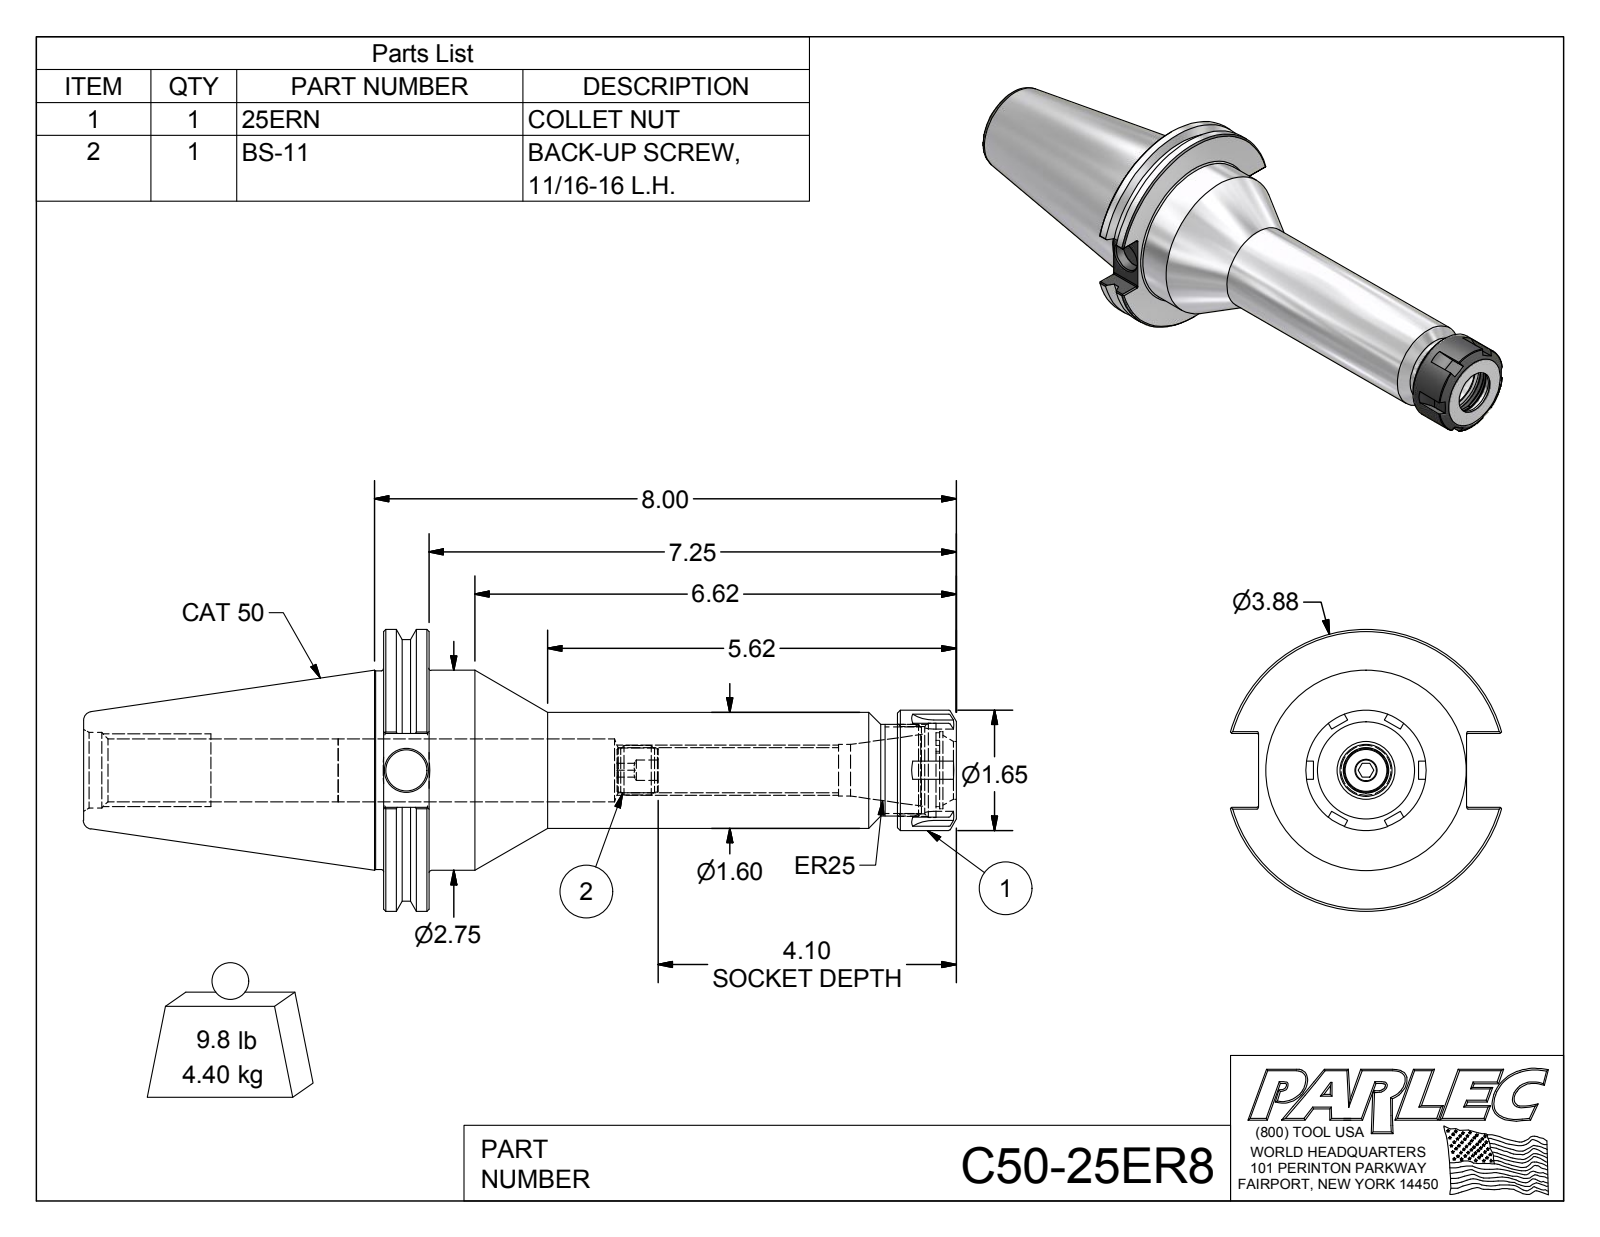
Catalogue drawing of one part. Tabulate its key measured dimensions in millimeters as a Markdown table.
| quantity | value |
| --- | --- |
| part name | C50-25ER8; C50-25ER8-1; 25ERN; BS-11 |
| STEP written by | Autodesk Inventor 2012 (AUTOMOTIVE_DESIGN) |
| units | millimeters |
| bodies | 3 solids, 153 faces (63 planar, 48 cylindrical, 42 other) |
| overall size | 304.8 × 98.4 × 94.7 |
| volume | 567 300 mm³ |
| surface area | 83 870 mm² |
| round holes (diameter × count) | 7.1 × 1, 14.3 × 1, 15.7 × 1, 18 × 1, 20.2 × 1, 21.9 × 1, 22 × 1, 26.4 × 1, 26.8 × 1, 30.5 × 1, 32.9 × 1 |
| round bosses / shafts (diameter × count) | 98.4 × 1, 91.3 × 1, 69.9 × 1, 69.3 × 1, 42 × 1, 40.5 × 1, 32 × 1, 17.3 × 1 |
| partial cylindrical surfaces (radius × count) | 0.5 × 12, 12.7 × 6, 12 × 1, 13.1 × 1 |
| main face-to-face distances | 15.9, 200, 184.2, 179.5, 163.7, 20.5, 193, 177.1, 13.5, 7 |
